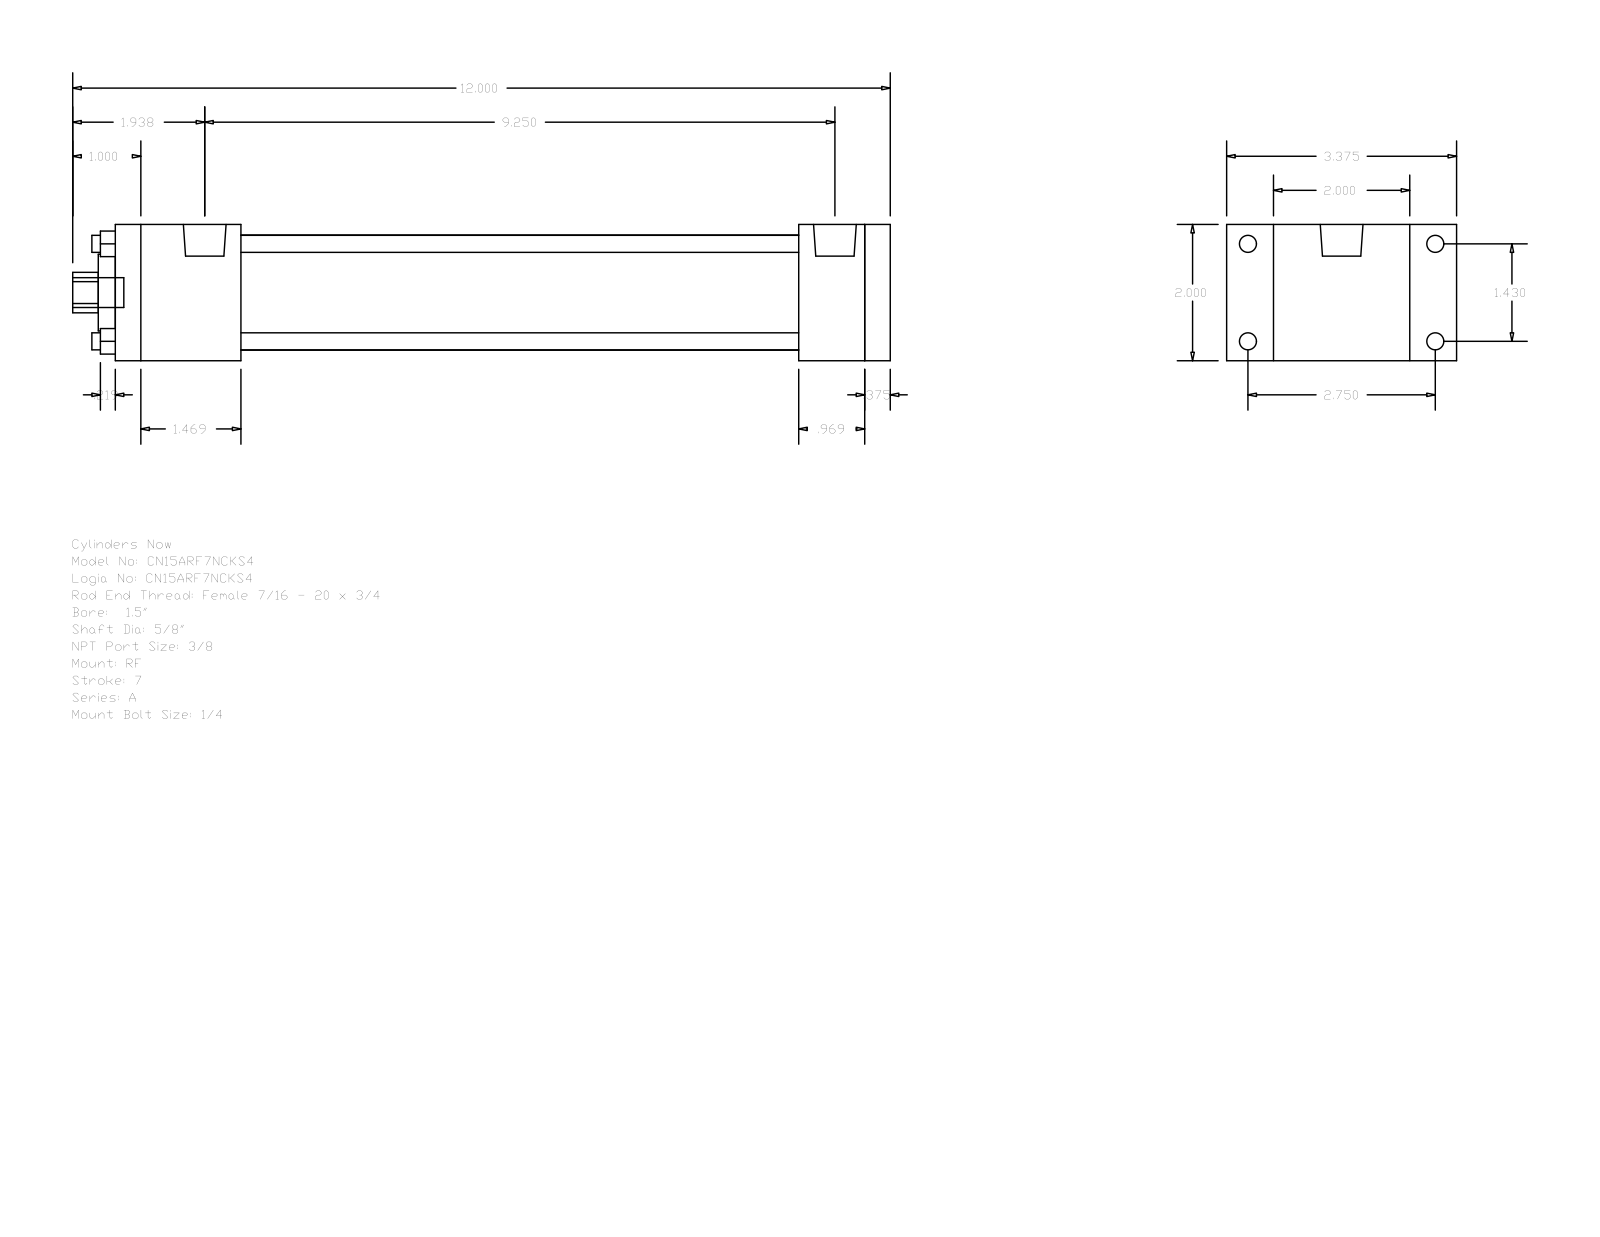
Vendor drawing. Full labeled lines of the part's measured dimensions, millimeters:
Part name (STEP PRODUCT): A_RF__0150_0.625
STEP written by: GSSL Pune (CONFIG_CONTROL_DESIGN)
Units: millimetres
Bodies: 0 solids, 92 faces (64 planar, 28 cylindrical, 0 other)
Overall size (bounding box): 304.8 × 85.72 × 50.8
Round holes (diameter × count): ⌀6.35 ×4, ⌀15.88 ×1, ⌀28.57 ×1, ⌀42.93 ×1
Round bosses / shafts (diameter × count): ⌀6.35 ×4, ⌀5.56 ×4, ⌀15.93 ×2, ⌀11.11 ×1
Partial cylindrical surfaces — rounded edges, fillets, slot ends (radius × count): R7.54 ×1
Main face-to-face distances: 50.8, 9.53, 288.92, 279.39, 254.79, 24.6, 34.13, 46.83, 207.96, 232.56
Hole centre spacings: 25.68, 36.32, 51.36
